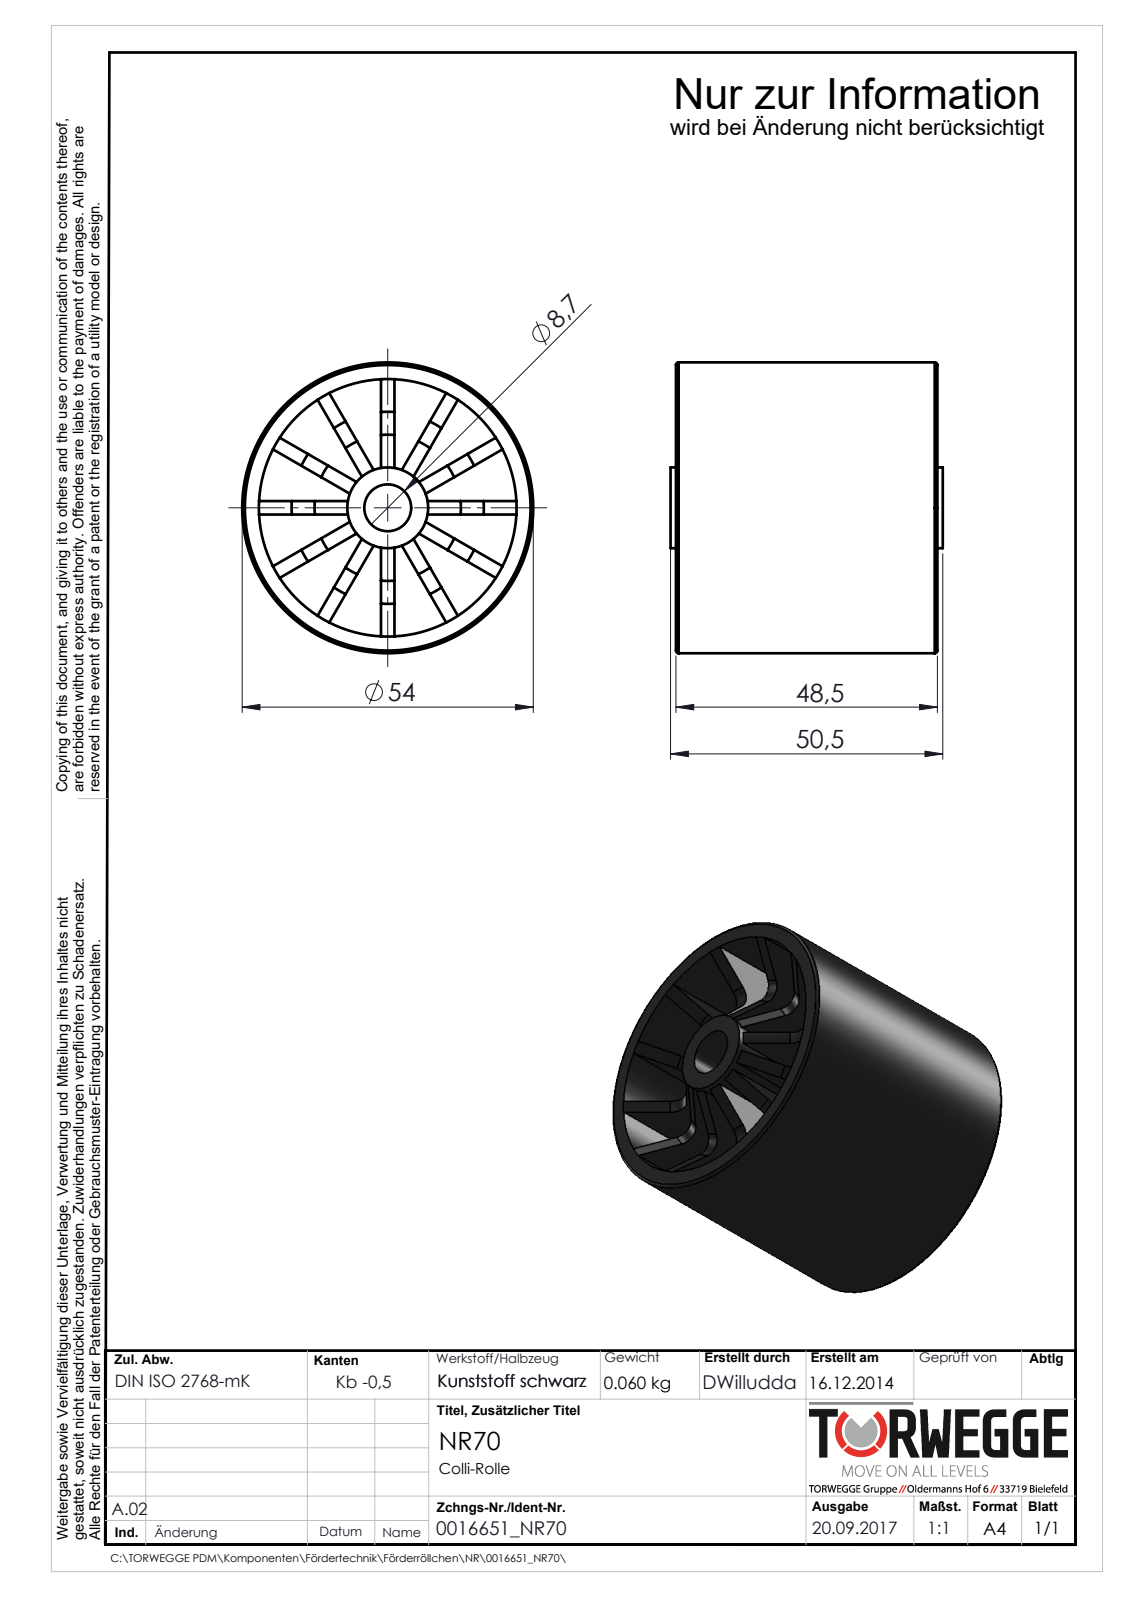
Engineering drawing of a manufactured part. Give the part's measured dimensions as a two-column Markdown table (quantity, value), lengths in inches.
| quantity | value |
| --- | --- |
| part name | 0016651_NR70 |
| STEP written by | SolidWorks 2016 (AUTOMOTIVE_DESIGN) |
| units | inches |
| bodies | 1 solid, 190 faces (76 planar, 32 cylindrical, 82 other) |
| overall size | 2.126 × 2.126 × 1.988 |
| volume | 3.216 in³ |
| surface area | 55.41 in² |
| round holes (diameter × count) | 0.343 × 1, 1.882 × 1 |
| round bosses / shafts (diameter × count) | 2.126 × 1, 0.591 × 1 |
| main face-to-face distances | 0.098, 0.906, 1.004, 1.909, 0.039, 0.945, 1.043, 1.949, 1.988 |
